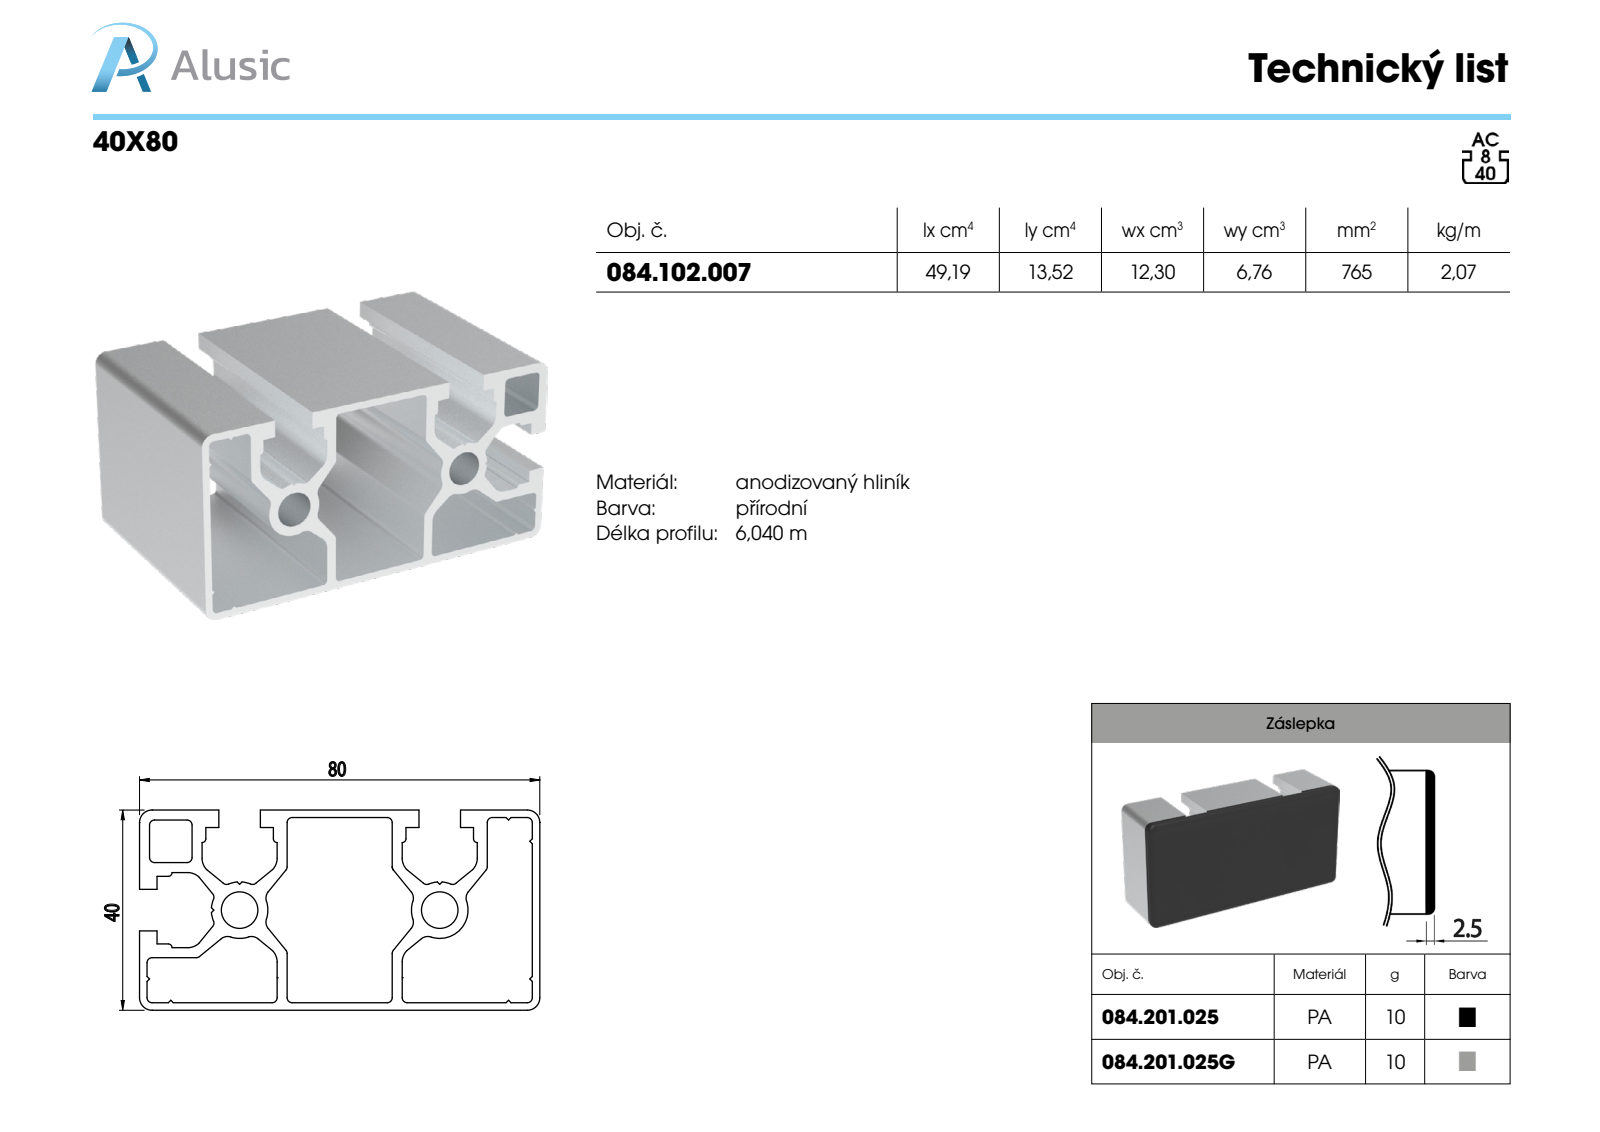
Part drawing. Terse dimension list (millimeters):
name: 084.102.007
written by: SolidWorks 2011 (CONFIG_CONTROL_DESIGN)
unit: mm
bodies: 1 solid, 163 faces (90 planar, 73 cylindrical, 0 other)
size: 100 × 80 × 40
volume: 76 458 mm³; area: 75 443 mm²
holes: 2× ⌀7.3
rounds: 27× R1, 8× R2, 8× R3.2, 6× R0.75, 4× R2.5, 2× R5.65
face distances: 1.5, 40, 38.5, 2, 29.5, 50.5, 27.5, 28, 10.5, 26
hole spacings: 40
